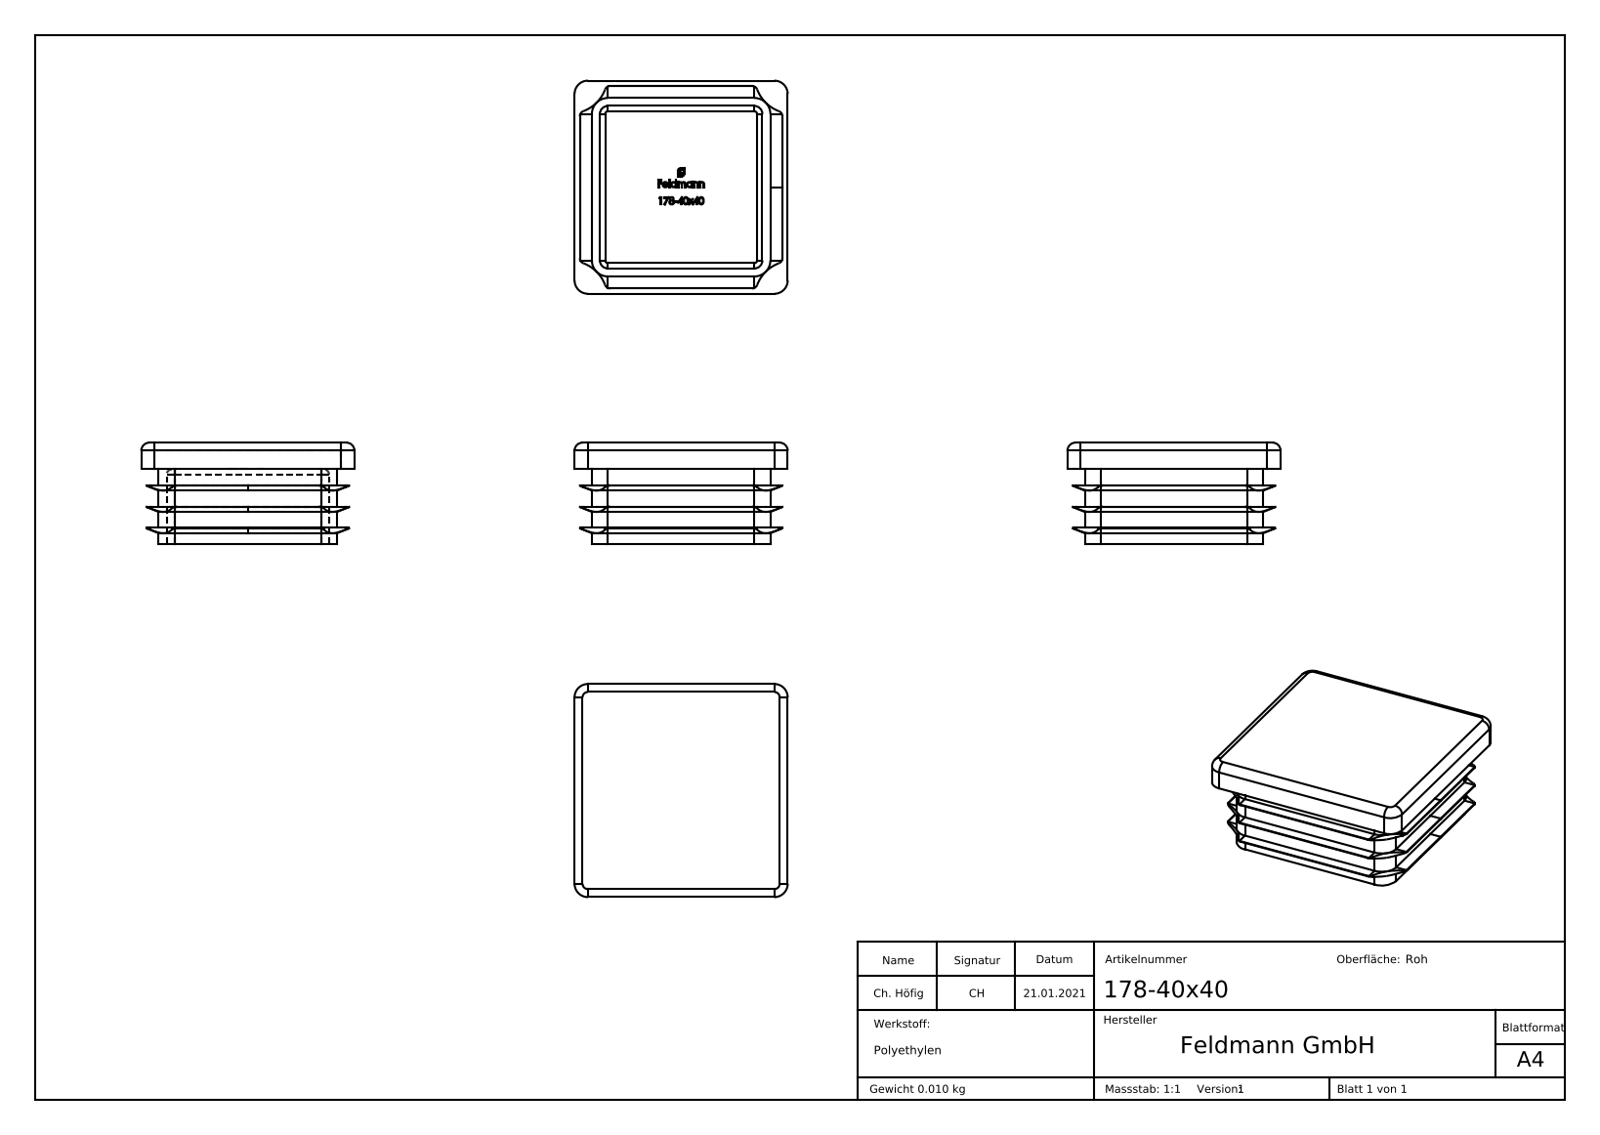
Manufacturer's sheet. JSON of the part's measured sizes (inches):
{"part_name": "178-40x40", "step_written_by": "SolidWorks 2018 (CONFIG_CONTROL_DESIGN)", "units": "inches", "bodies": {"solids": 1, "faces": 465, "planar": 235, "cylindrical": 83, "other": 147}, "overall_size": [1.575, 1.575, 0.748], "volume_in3": 0.669, "surface_area_in2": 13.37, "partial_cylinders_radius": [[0.039, 12], [0.059, 8], [0.098, 4], [0.118, 4], [0.276, 4]], "face_to_face_distances": [0.197, 0.059, 1.26, 1.201, 1.319, 0.157, 0.315, 0.128, 0.187, 1.388]}
